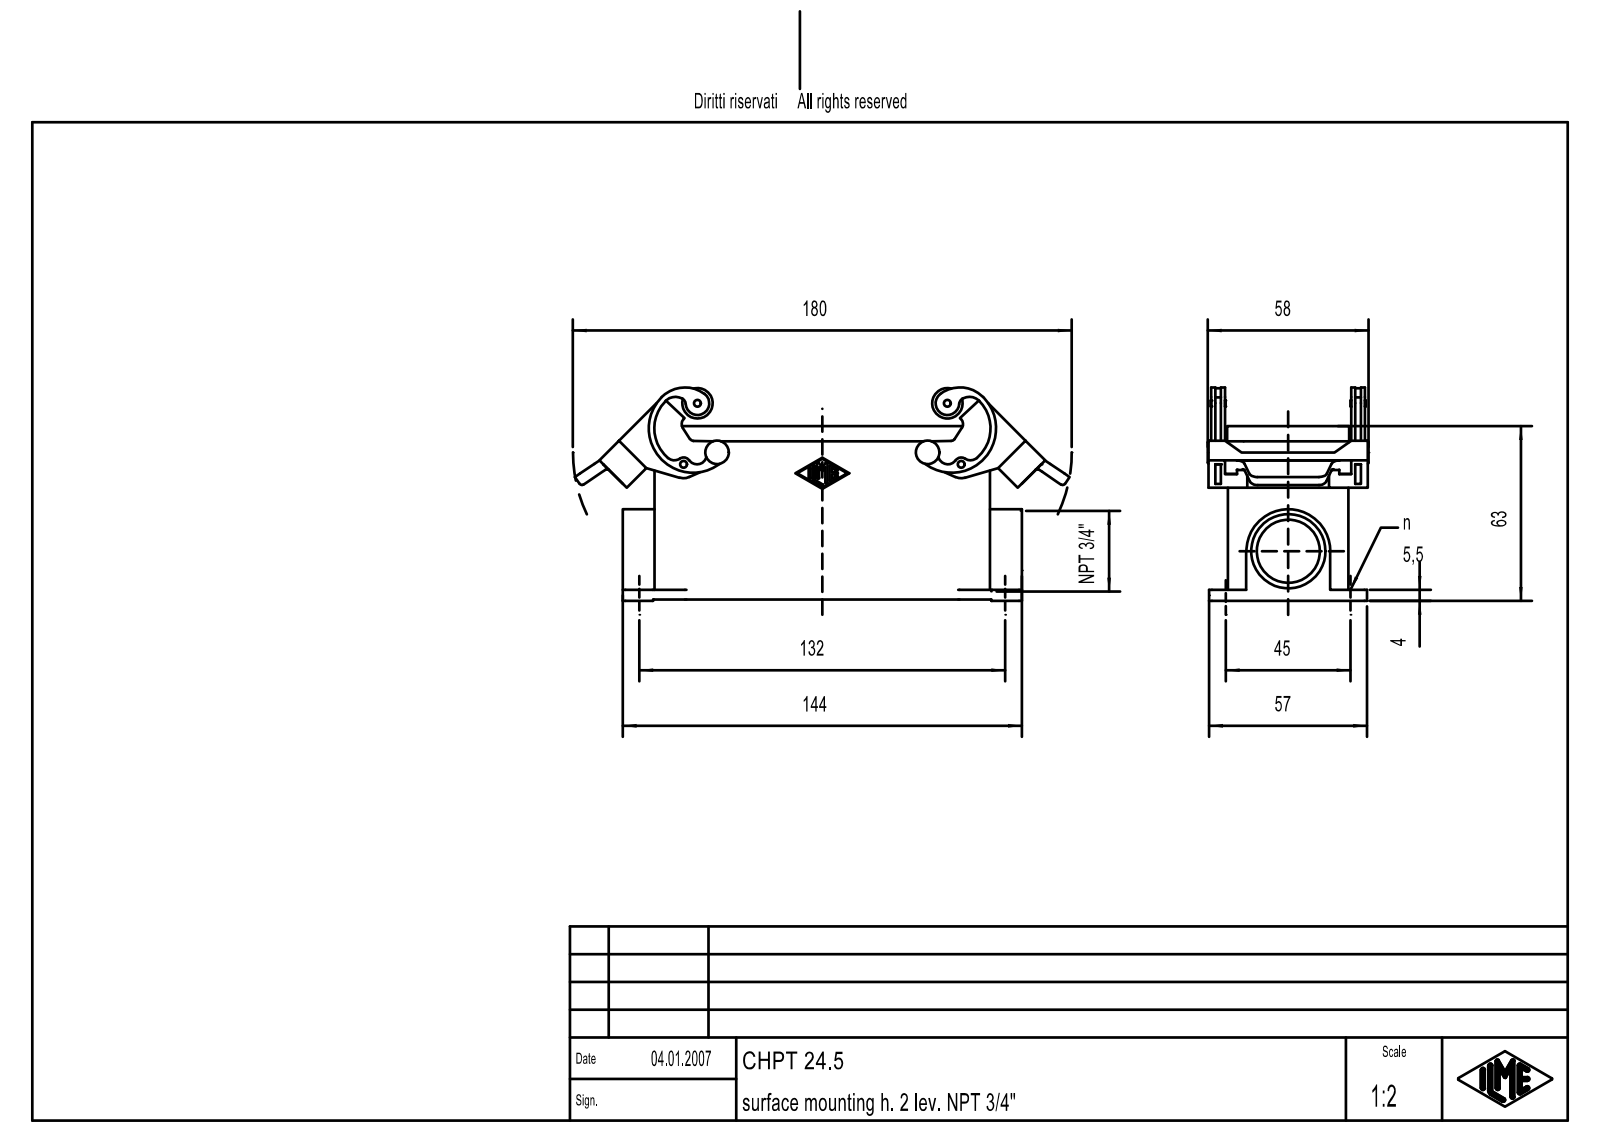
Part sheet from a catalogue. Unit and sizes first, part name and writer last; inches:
Units: inches
Overall size (bounding box): 7.027 × 3.698 × 2.283
Round holes (diameter × count): ⌀0.079 ×4, ⌀0.097 ×4, ⌀0.122 ×4, ⌀0.217 ×4, ⌀0.897 ×1, ⌀1.054 ×1
Round bosses / shafts (diameter × count): ⌀0.433 ×2, ⌀0.197 ×2, ⌀0.118 ×2, ⌀0.098 ×2
Partial cylindrical surfaces — rounded edges, fillets, slot ends (radius × count): R0.039 ×20, R0.015 ×14, R0.118 ×12, R0.236 ×8, R0.059 ×6, R0.098 ×6, R0.079 ×4, R0.138 ×4
Main face-to-face distances: 0.118, 1.594, 1.713, 1.476, 0.138, 0.157, 1.988, 0.433, 0.177, 4.331
Hole centre spacings: 0.655, 1.521, 4.659, 4.857, 0.888, 1.063, 1.772, 3.845
Bodies: 6 solids, 666 faces (328 planar, 256 cylindrical, 82 other)
Part name (STEP PRODUCT): CAP_24.21
STEP written by: Creo Elements/Direct Modeling 18.0B 02-Dec-2011 (C) Parametric Technology GmbH (AUTOMOTIVE_DESIGN)
